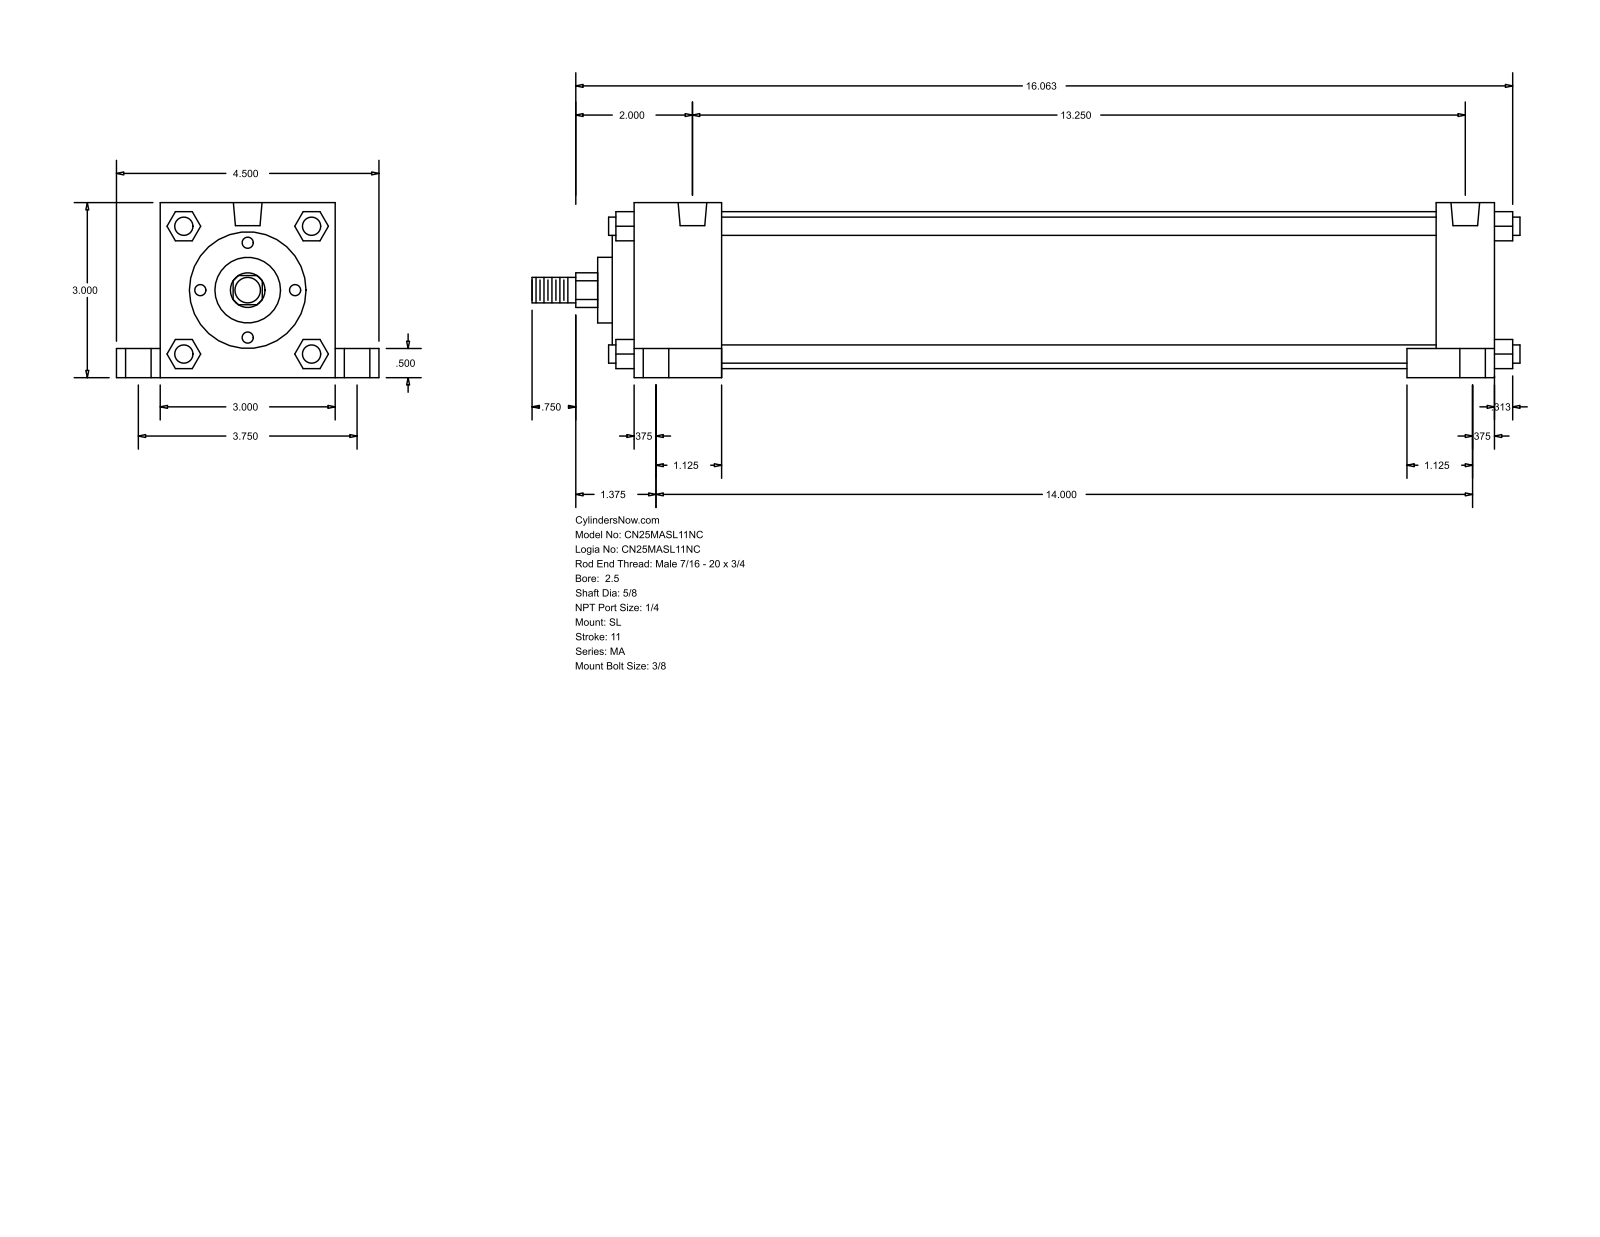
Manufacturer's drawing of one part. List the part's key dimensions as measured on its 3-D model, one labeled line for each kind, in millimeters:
Part name (STEP PRODUCT): MA_SL__0250_0.625
STEP written by: GSSL Pune (CONFIG_CONTROL_DESIGN)
Units: millimetres
Bodies: 0 solids, 150 faces (113 planar, 37 cylindrical, 0 other)
Overall size (bounding box): 430.21 × 114.3 × 76.2
Round holes (diameter × count): ⌀7.94 ×4, ⌀11.11 ×4, ⌀17.46 ×4, ⌀12.49 ×2
Round bosses / shafts (diameter × count): ⌀7.94 ×4, ⌀68.33 ×1, ⌀50.8 ×1, ⌀28.57 ×1, ⌀15.88 ×1, ⌀11.11 ×1
Partial cylindrical surfaces — rounded edges, fillets, slot ends (radius × count): R7.54 ×1
Main face-to-face distances: 76.2, 374.65, 12.7, 311.15, 25.4, 38.1, 336.55, 349.25, 19.05, 63.5
Hole centre spacings: 47.73, 50.2, 95.24, 336.55, 343.04, 355.6, 355.63, 368.13
